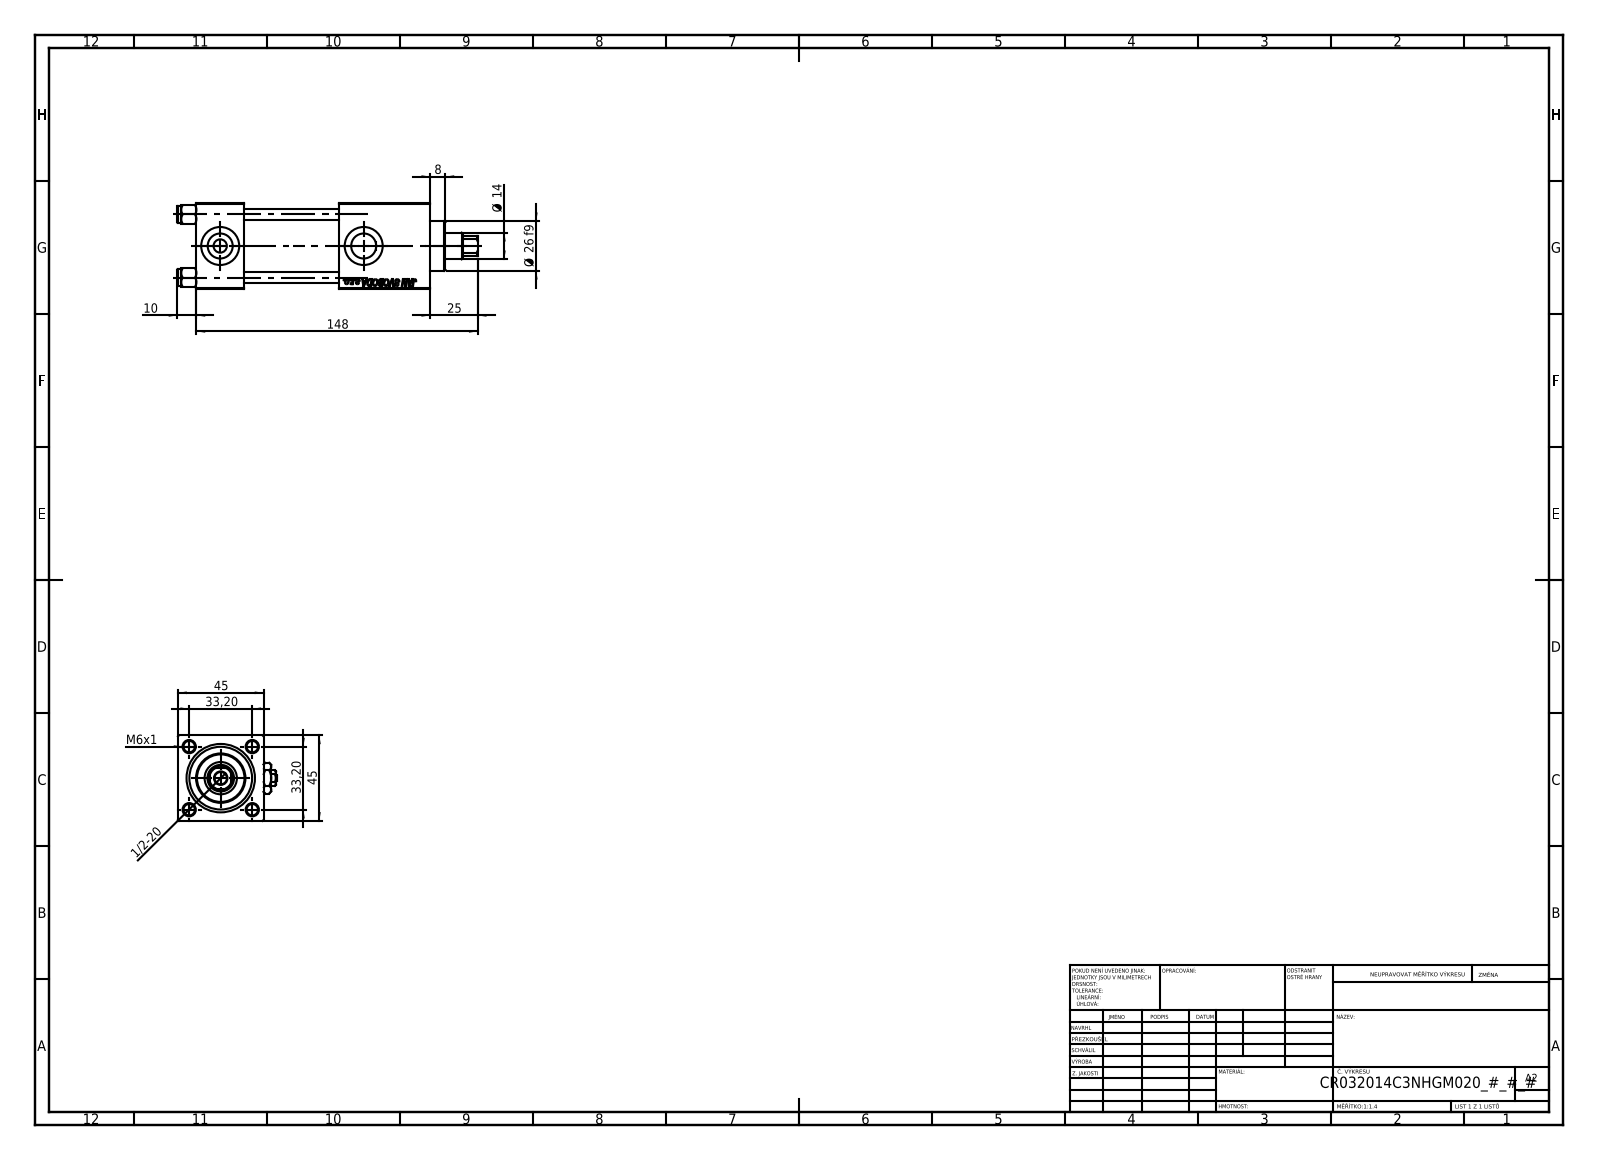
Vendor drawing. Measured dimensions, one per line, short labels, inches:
name: NUT_M5_C; V215CR_C_TYCINKA; Zatka_pro_OIL_PORT; V215_VC_A (+2 more)
written by: SolidWorks 2019 (CONFIG_CONTROL_DESIGN)
unit: in
bodies: 13 solids, 1248 faces (572 planar, 98 cylindrical, 578 other)
size: 6.22 × 2.047 × 1.772
volume: 11.74 in³; area: 106.8 in²
holes: 4× ⌀0.236, 2× ⌀0.276, 2× ⌀0.518, 2× ⌀0.787, 1× ⌀0.256, 1× ⌀0.551, 1× ⌀0.669, 1× ⌀0.945, 1× ⌀1.26, 1× ⌀1.299
bosses: 4× ⌀0.354, 1× ⌀1.496, 1× ⌀1.024
rounds: 1× R0.256
face distances: 1.772, 0.984, 3.858, 4.843, 1.969, 2.953, 1.89, 3.713, 2.728, 0.76
hole spacings: 0.924, 1.307, 1.848, 2.972
